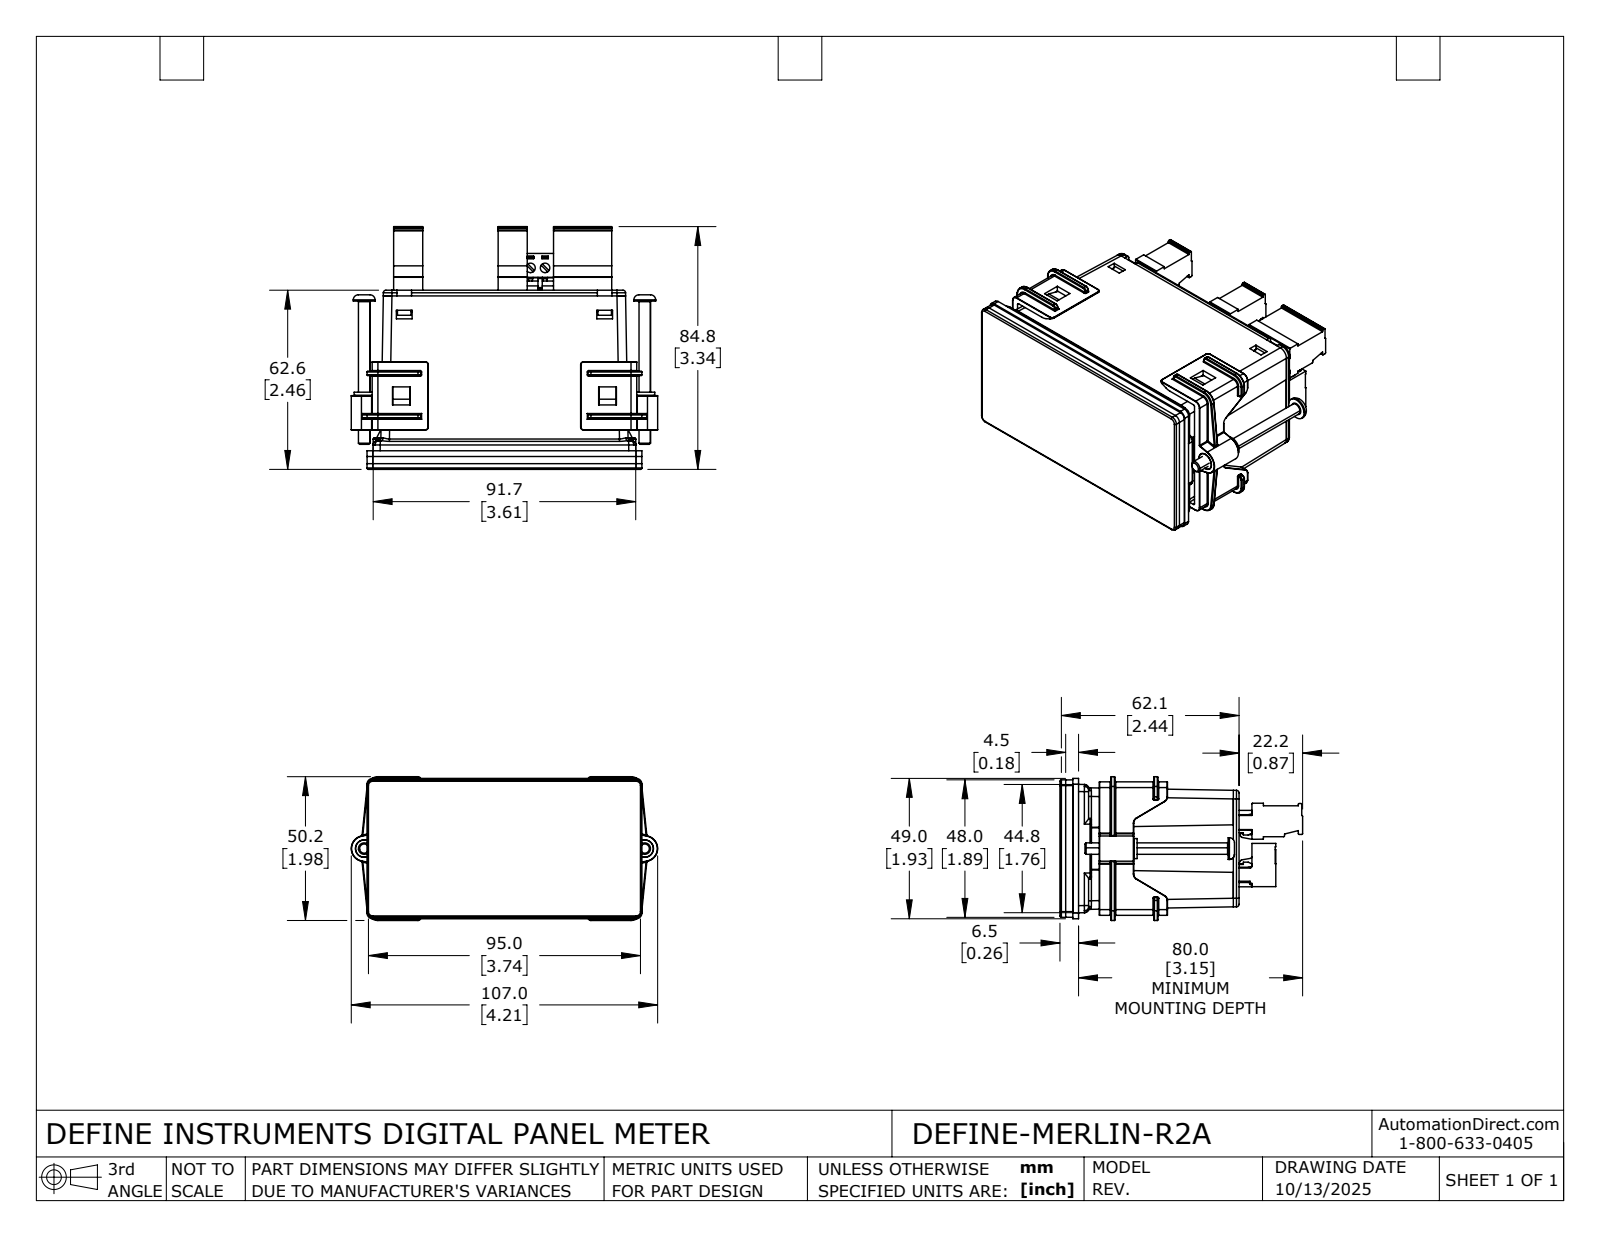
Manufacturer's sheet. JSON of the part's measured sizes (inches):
{"part_name": "DEFINE-MERLIN-R2A", "step_written_by": "SolidWorks 2024 (AUTOMOTIVE_DESIGN)", "units": "inches", "bodies": {"solids": 20, "faces": 5859, "planar": 4132, "cylindrical": 1215, "other": 512}, "overall_size": [4.213, 3.337, 1.976], "volume_in3": 5.235, "surface_area_in2": 126.9, "round_holes": [[0.047, 8], [0.059, 8], [0.094, 8], [0.118, 8], [0.131, 8], [0.152, 8], [0.128, 2], [0.24, 2], [0.177, 1]], "round_bosses_or_shafts": [[0.299, 2], [0.276, 2], [0.236, 2], [0.157, 2]], "partial_cylinders_radius": [[0.006, 136], [0.01, 100], [0.004, 49], [0.02, 46], [0.008, 37], [0.012, 32], [0.039, 24], [0.079, 20]], "face_to_face_distances": [0.079, 1.535, 0.098, 2.226, 2.305, 0.177, 2.384, 2.128, 2.207, 2.325], "hole_center_spacings": [0.2, 0.4, 0.201, 0.016, 0.6, 2.198, 2.398, 2.598]}
